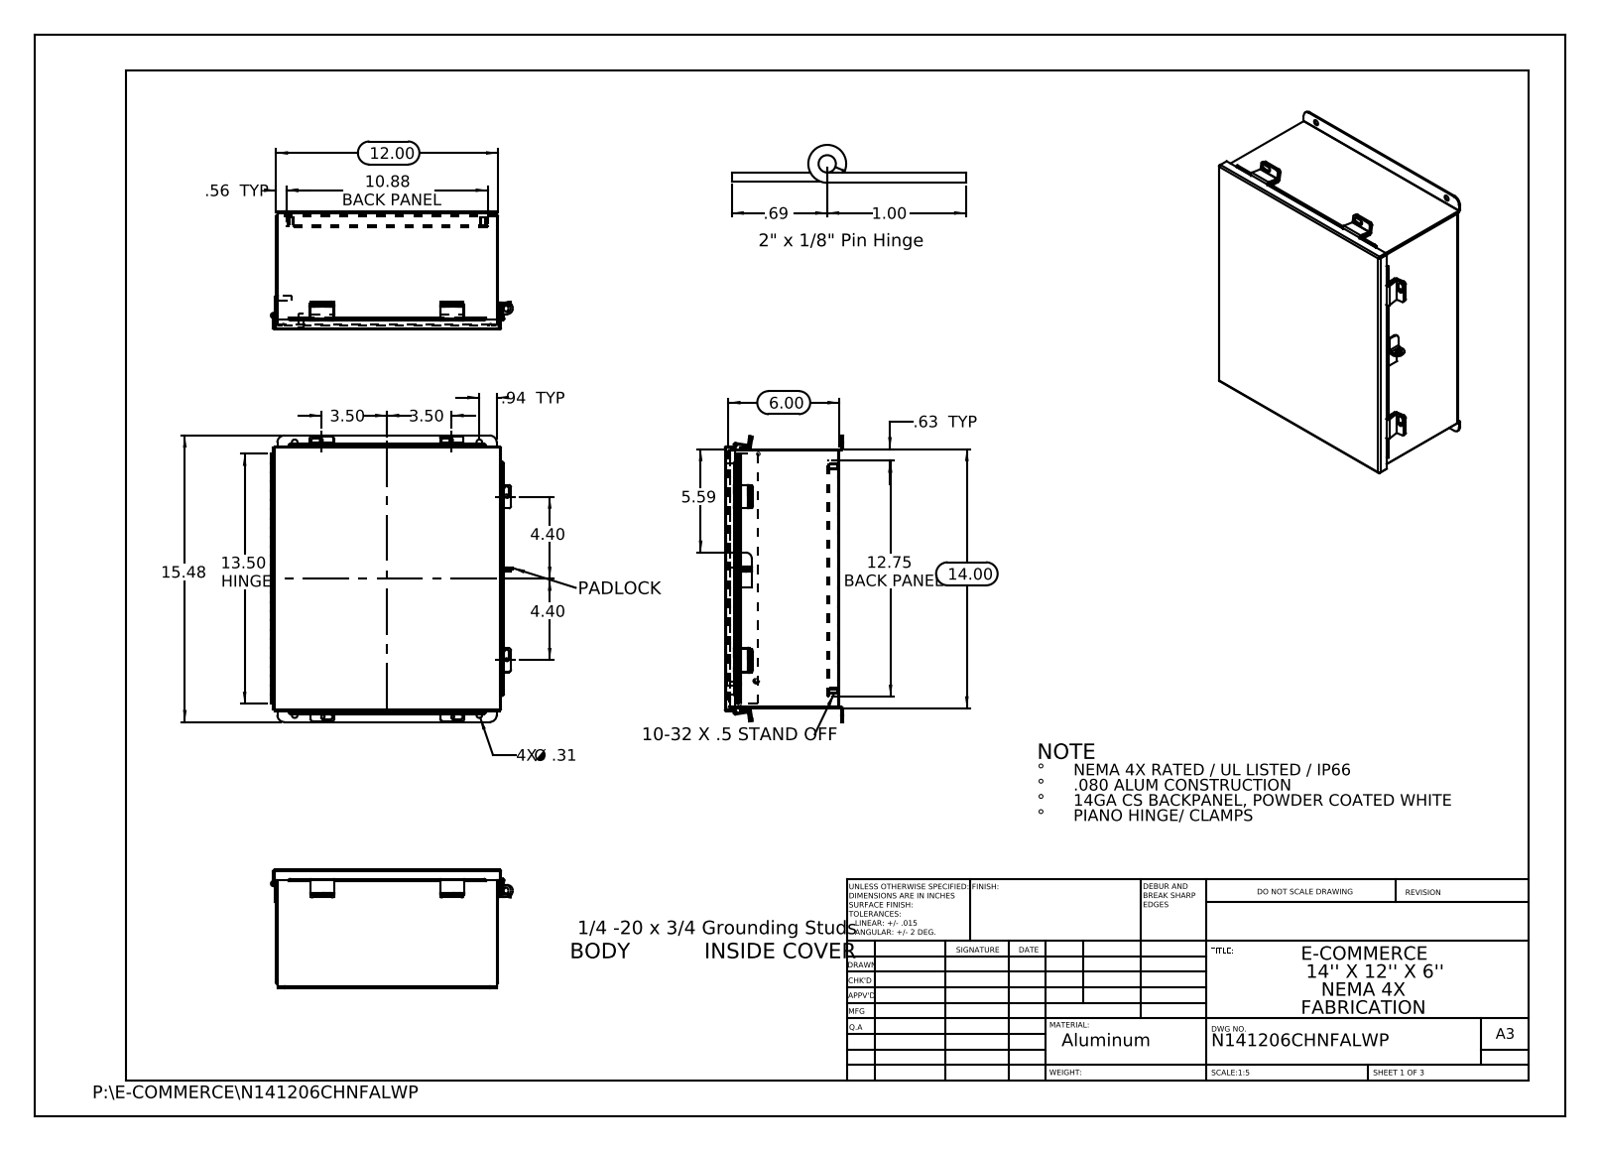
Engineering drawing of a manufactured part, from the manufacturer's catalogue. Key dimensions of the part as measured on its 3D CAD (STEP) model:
Part name (STEP PRODUCT): N141206CHNFALWP JIC Clamp Bracket; N141206CHNFALWP JIC Backpanel; N141206CHNFALWP JIC_Standoff; N141206CHNFALWP JIC_Cover_Template (+8 more)
STEP written by: SolidWorks 2013 (CONFIG_CONTROL_DESIGN)
Units: inches
Bodies: 27 solids, 830 faces (519 planar, 291 cylindrical, 20 other)
Overall size (bounding box): 15.476 × 13.072 × 6.39
Volume: 67.44 in³ · Surface area: 1 838 in²
Round holes (diameter × count): ⌀0.25 ×10, ⌀0.187 ×4, ⌀0.312 ×4, ⌀0.125 ×1, ⌀0.125 ×1, ⌀0.373 ×1, ⌀0.375 ×1
Round bosses / shafts (diameter × count): ⌀0.313 ×4, ⌀0.315 ×2, ⌀0.236 ×2, ⌀0.273 ×1, ⌀0.25 ×1
Partial cylindrical surfaces — rounded edges, fillets, slot ends (radius × count): R0.125 ×21, R0.013 ×13, R0.009 ×12, R0.088 ×12, R0.133 ×12, R0.083 ×6, R0.1 ×6, R0.375 ×4
Main face-to-face distances: 0.075, 6.128, 6.053, 6.203, 11.925, 13.925, 0.074, 0.575, 0.5, 5.553
Hole centre spacings: 1.315, 10.258, 13.428, 16.846, 7, 9.976, 10.375, 12.126
